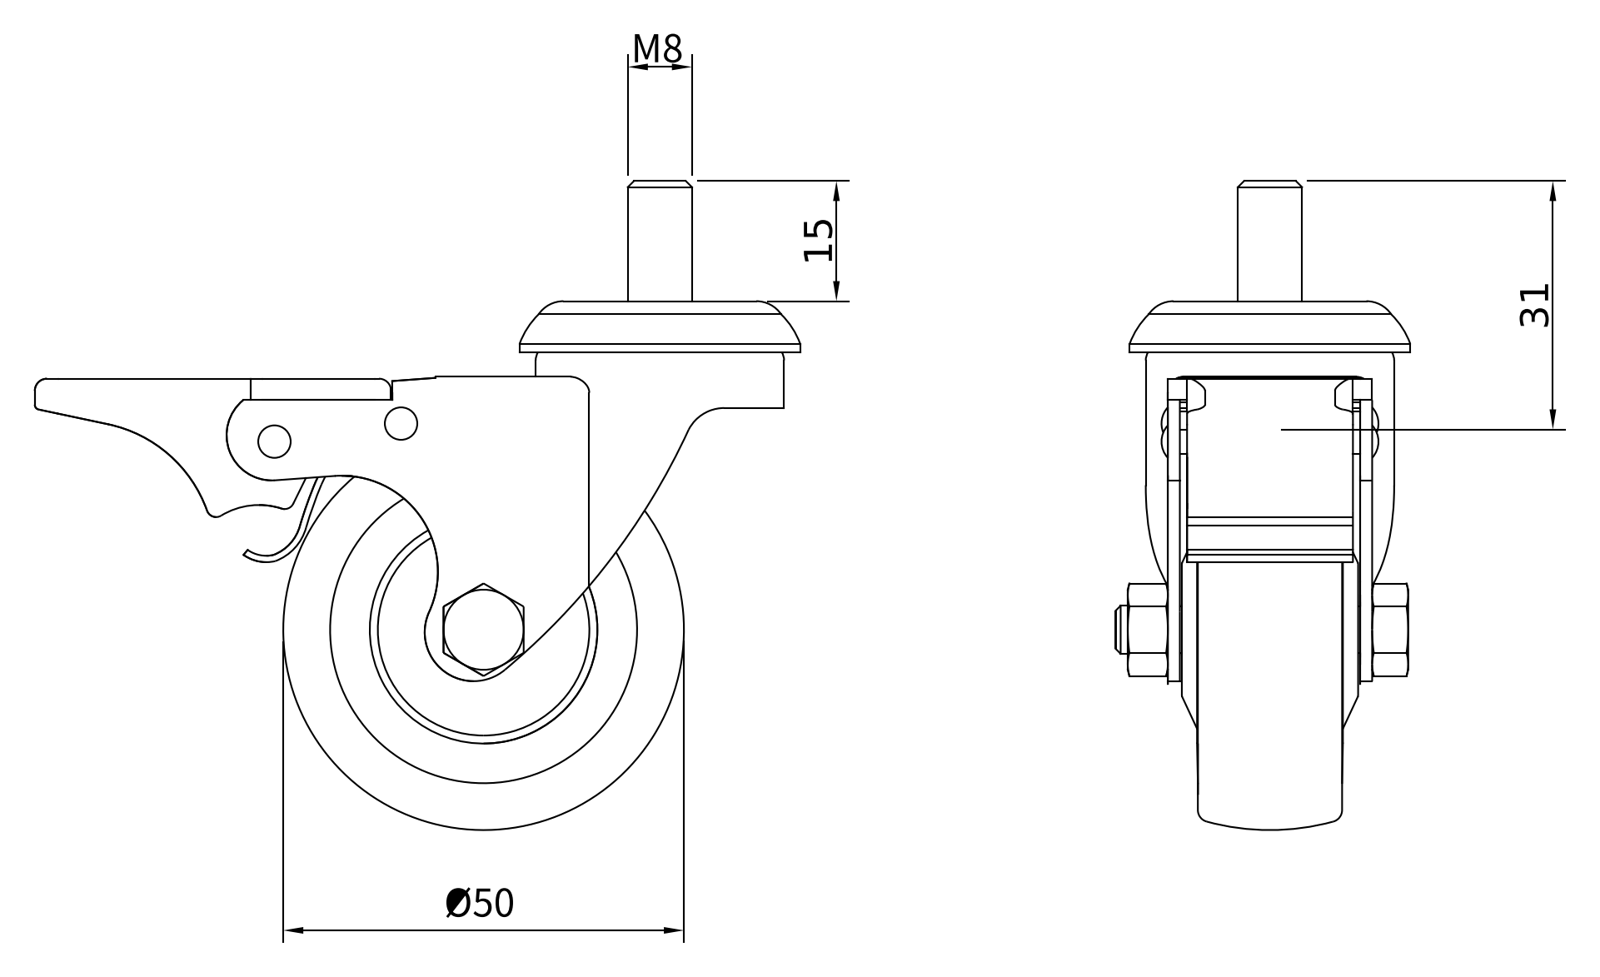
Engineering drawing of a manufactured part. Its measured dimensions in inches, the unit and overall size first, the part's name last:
Units: inches
Overall size (bounding box): 3.76 × 3.189 × 1.447
Round holes (diameter × count): ⌀0.194 ×1, ⌀0.236 ×1, ⌀0.248 ×1, ⌀0.315 ×1, ⌀1 ×1, ⌀1.102 ×1, ⌀1.118 ×1
Round bosses / shafts (diameter × count): ⌀0.118 ×2, ⌀1.378 ×1, ⌀1.22 ×1, ⌀1.039 ×1, ⌀0.63 ×1, ⌀0.315 ×1, ⌀0.311 ×1, ⌀0.28 ×1
Partial cylindrical surfaces — rounded edges, fillets, slot ends (radius × count): R0.059 ×4, R0.079 ×4, R0.02 ×2, R0.118 ×2, R3.425 ×2, R0.024 ×1, R0.047 ×1, R0.048 ×1
Main face-to-face distances: 0.059, 0.945, 0.089, 0.856, 0.094, 1.004, 0.909, 0.035, 0.85, 0.148
Volume: 3.38 in³ · Surface area: 42.53 in²
Bodies: 8 solids, 201 faces (73 planar, 61 cylindrical, 67 other)
Part name (STEP PRODUCT): CRUST0000017; 440000025803; 440000025804; 440000025805 (+4 more)
STEP written by: Autodesk Inventor 2022 (AUTOMOTIVE_DESIGN)
